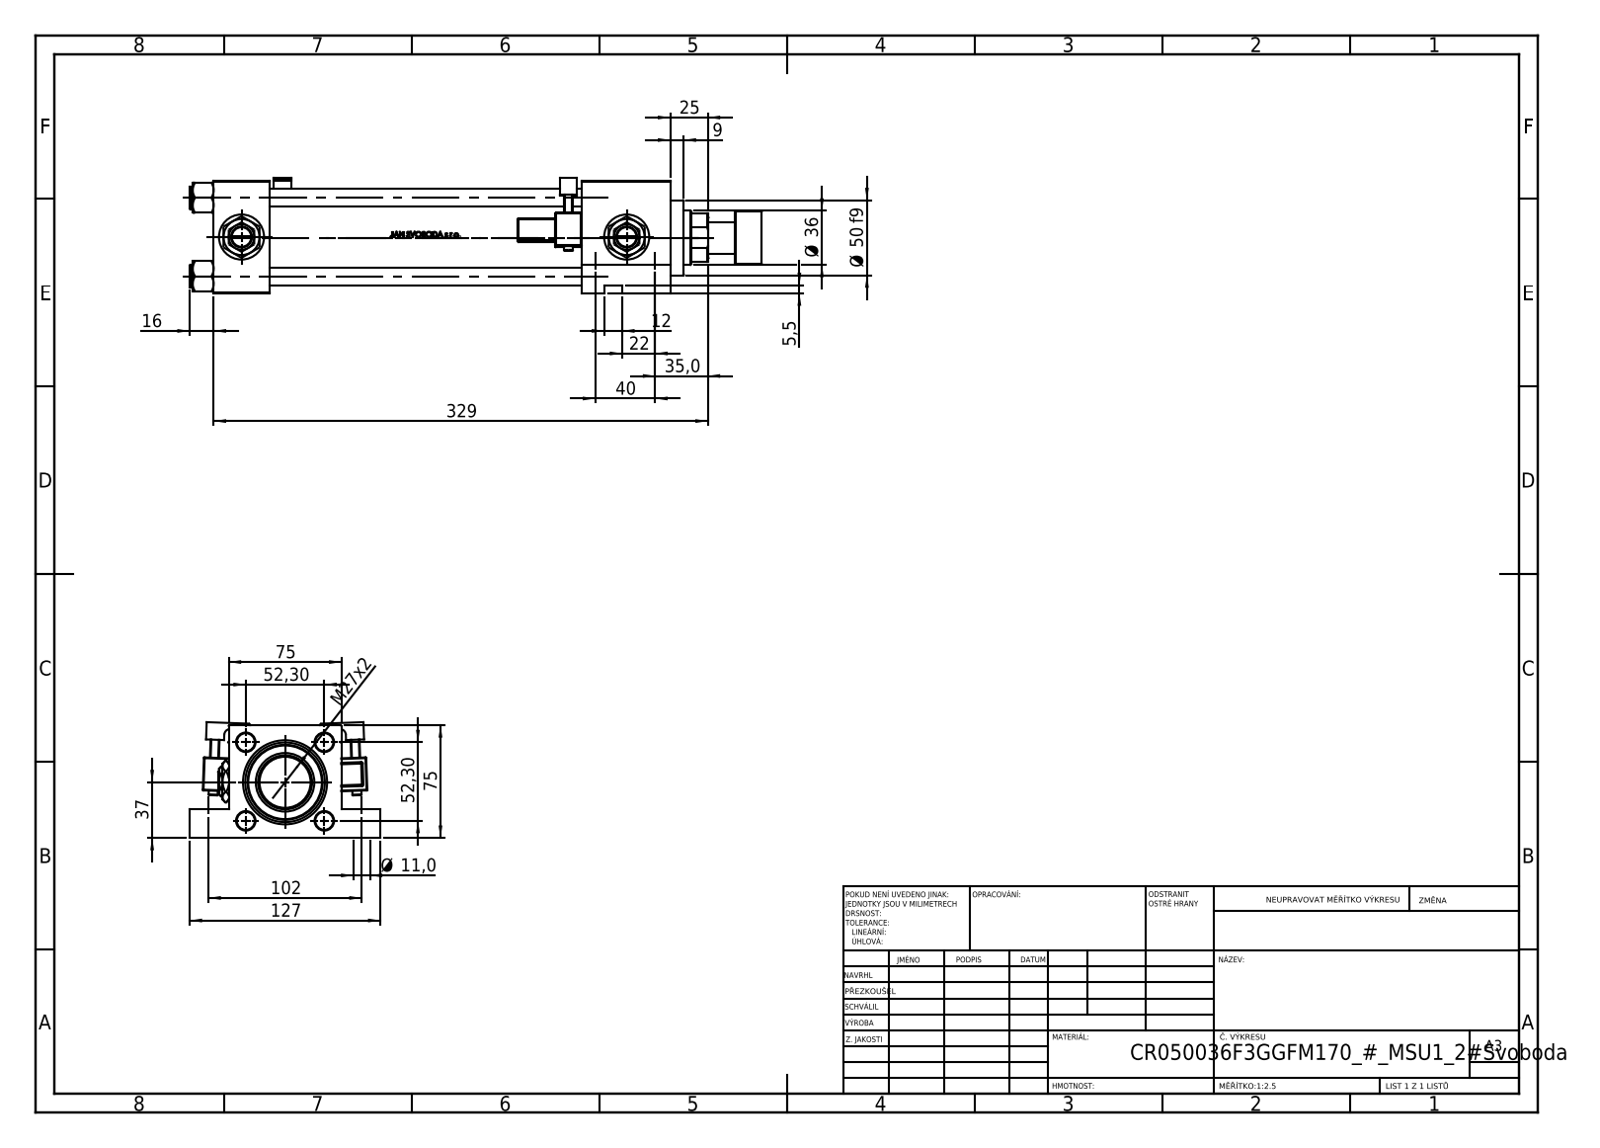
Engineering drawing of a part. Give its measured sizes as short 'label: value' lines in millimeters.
name: Zatka_pro_OIL_PORT; V215CR_MSU; V215CR_VCP_F; V215CR_F_TYCINKA (+4 more)
written by: SolidWorks 2019 (CONFIG_CONTROL_DESIGN)
unit: mm
bodies: 16 solids, 1370 faces (546 planar, 200 cylindrical, 624 other)
size: 381 × 127 × 77.03
volume: 1 090 000 mm³; area: 276 344 mm²
holes: 4× ⌀11, 4× ⌀12, 4× ⌀20.96, 4× ⌀30, 3× ⌀7, 1× ⌀25.5, 1× ⌀36, 1× ⌀39, 1× ⌀41, 1× ⌀53
bosses: 4× ⌀15, 2× ⌀6, 1× ⌀56, 1× ⌀50, 1× ⌀35, 1× ⌀21
rounds: 48× R0.5, 2× R1, 2× R2.5, 2× R4
face distances: 75, 37, 245, 208, 59, 304, 267, 19, 56, 74.8
hole spacings: 52.3, 36.63, 37.34, 40, 51.62, 60.21, 73.96, 102
